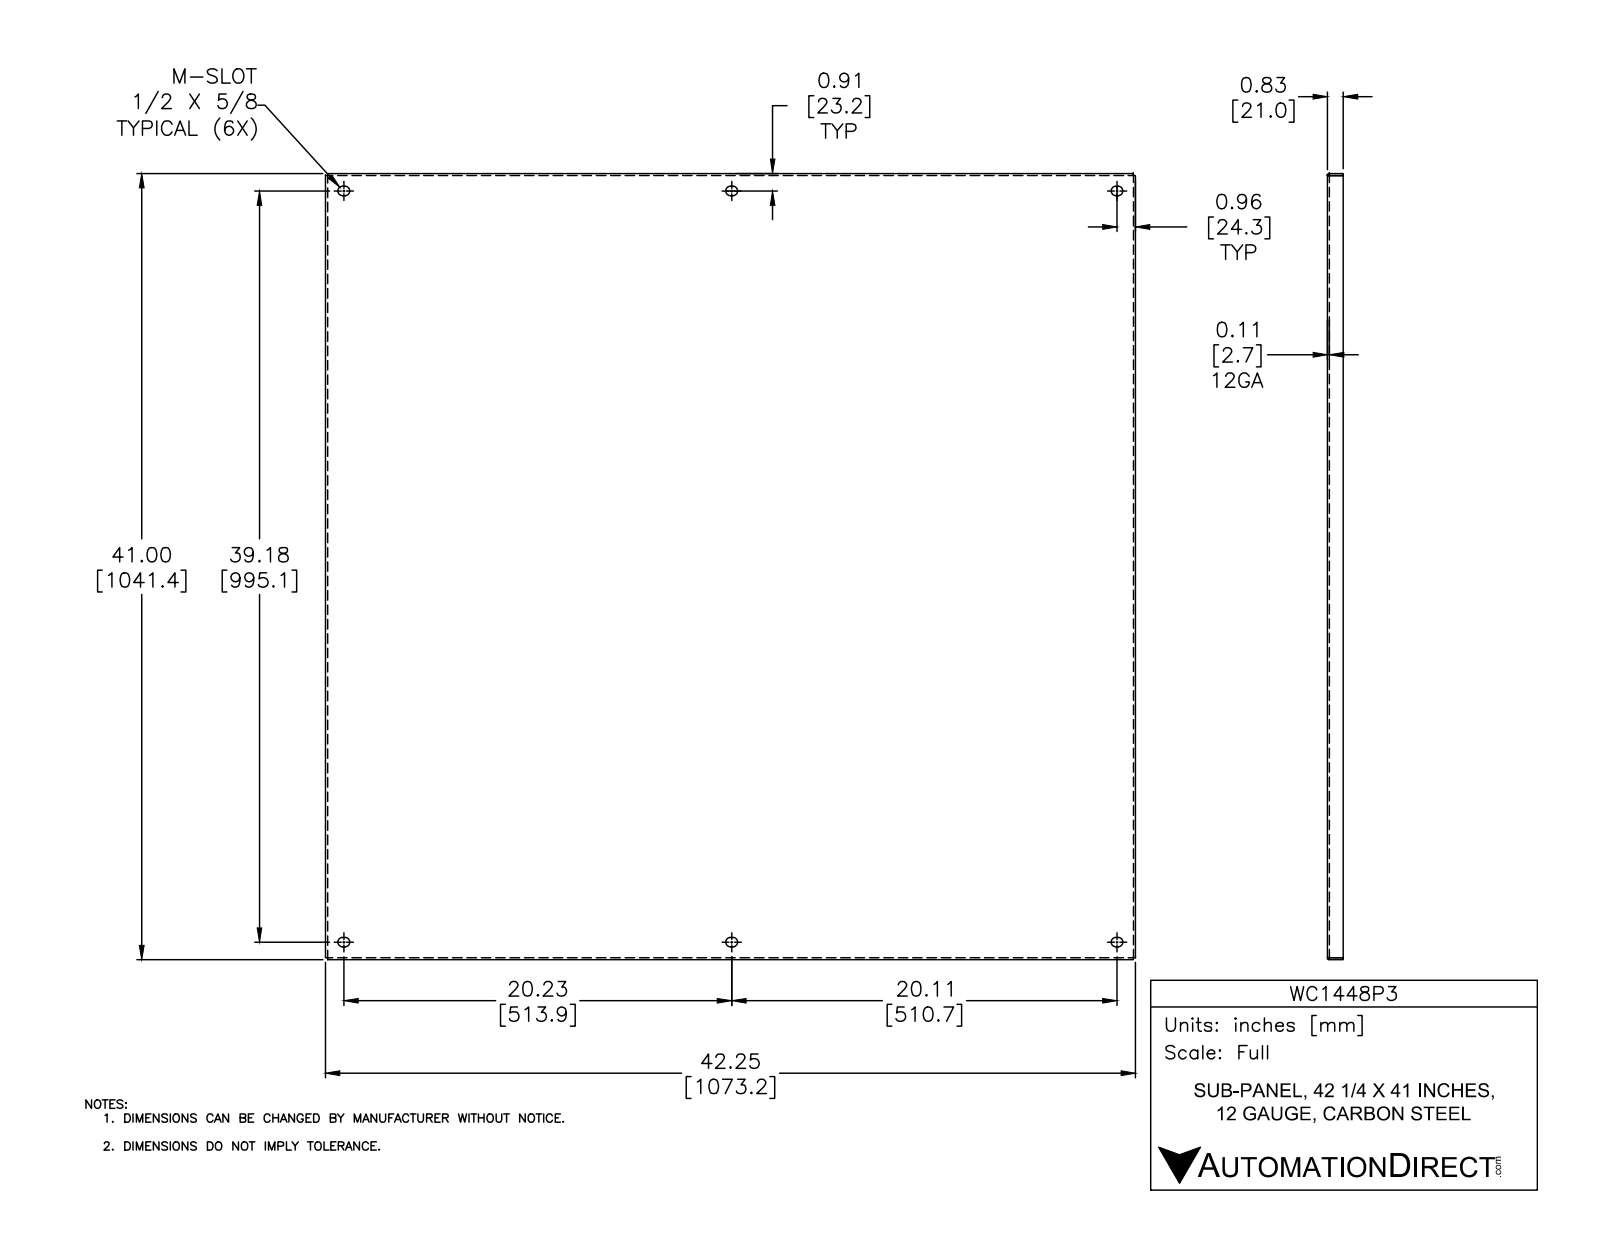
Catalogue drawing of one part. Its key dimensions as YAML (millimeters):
part_name: "WC1448P3"
step_written_by: "SolidWorks 2014 (AUTOMOTIVE_DESIGN)"
units: millimeters
bodies: {solids: 1, faces: 68, planar: 34, cylindrical: 26, other: 8}
overall_size: [1076.3, 1043, 21]
volume: 3179000
surface_area: 2405000
partial_cylinders:
  - {radius: 6.4, count: 12}
  - {radius: 2.7, count: 3}
  - {radius: 2.7, count: 1}
face_to_face_distances: [2.7, 1040.3, 1043, 1037.7, 2.6, 1073.7, 1076.3, 1071, 1073.7, 21]
